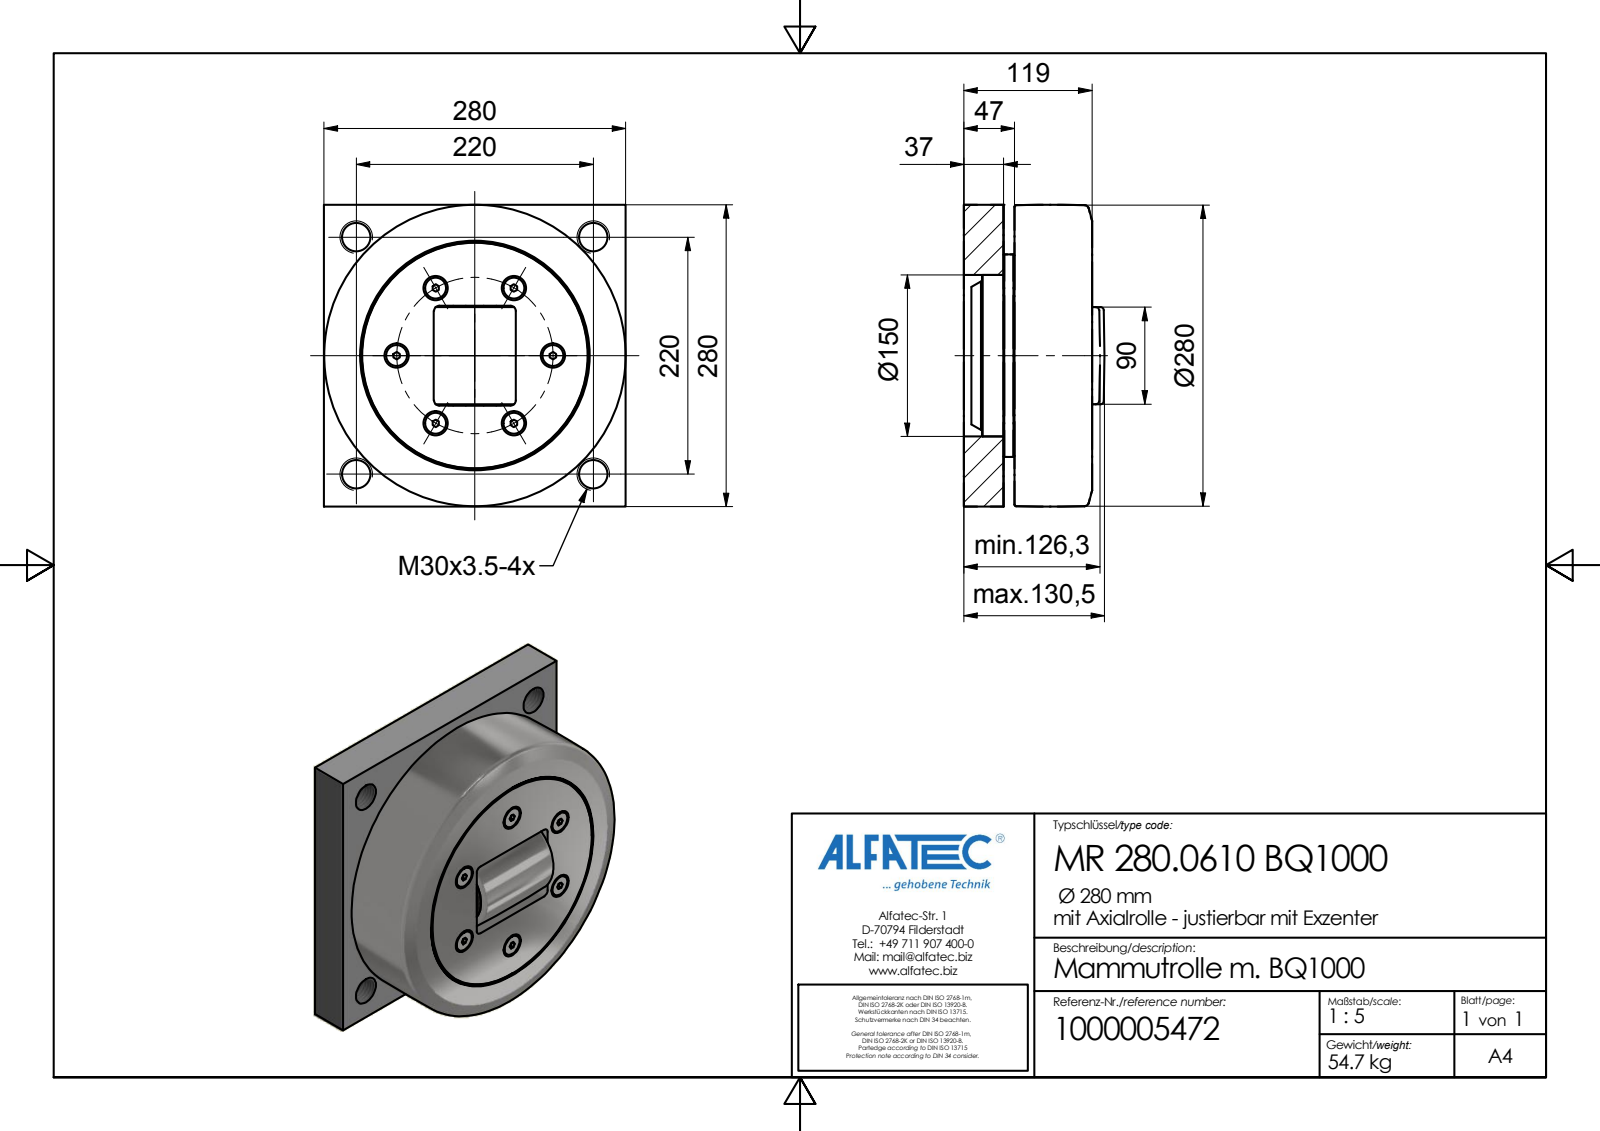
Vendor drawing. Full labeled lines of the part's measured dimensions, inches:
Part name (STEP PRODUCT): MR 280.0410 BQ1000_Kontur
STEP written by: Autodesk Inventor 2020 (AUTOMOTIVE_DESIGN)
Units: inches
Bodies: 1 solid, 179 faces (79 planar, 42 cylindrical, 58 other)
Overall size (bounding box): 11.024 × 11.024 × 4.685
Volume: 395.6 in³ · Surface area: 810.5 in²
Round holes (diameter × count): ⌀0.413 ×6, ⌀1.032 ×4, ⌀0.098 ×1, ⌀0.194 ×1, ⌀0.591 ×1, ⌀5.906 ×1, ⌀6.831 ×1, ⌀8.346 ×1, ⌀8.701 ×1
Round bosses / shafts (diameter × count): ⌀0.768 ×6, ⌀0.394 ×6, ⌀8.268 ×1, ⌀7.756 ×1, ⌀7.402 ×1, ⌀6.811 ×1, ⌀5.433 ×1, ⌀0.118 ×1
Partial cylindrical surfaces — rounded edges, fillets, slot ends (radius × count): R0.138 ×1
Main face-to-face distances: 1.457, 4.685, 3.228, 0.394, 1.85, 2.835, 4.26, 2.803, 2.409, 0.425
Hole centre spacings: 2.854, 2.854, 3.448, 4.576, 4.944, 6.05, 6.124, 8.389
